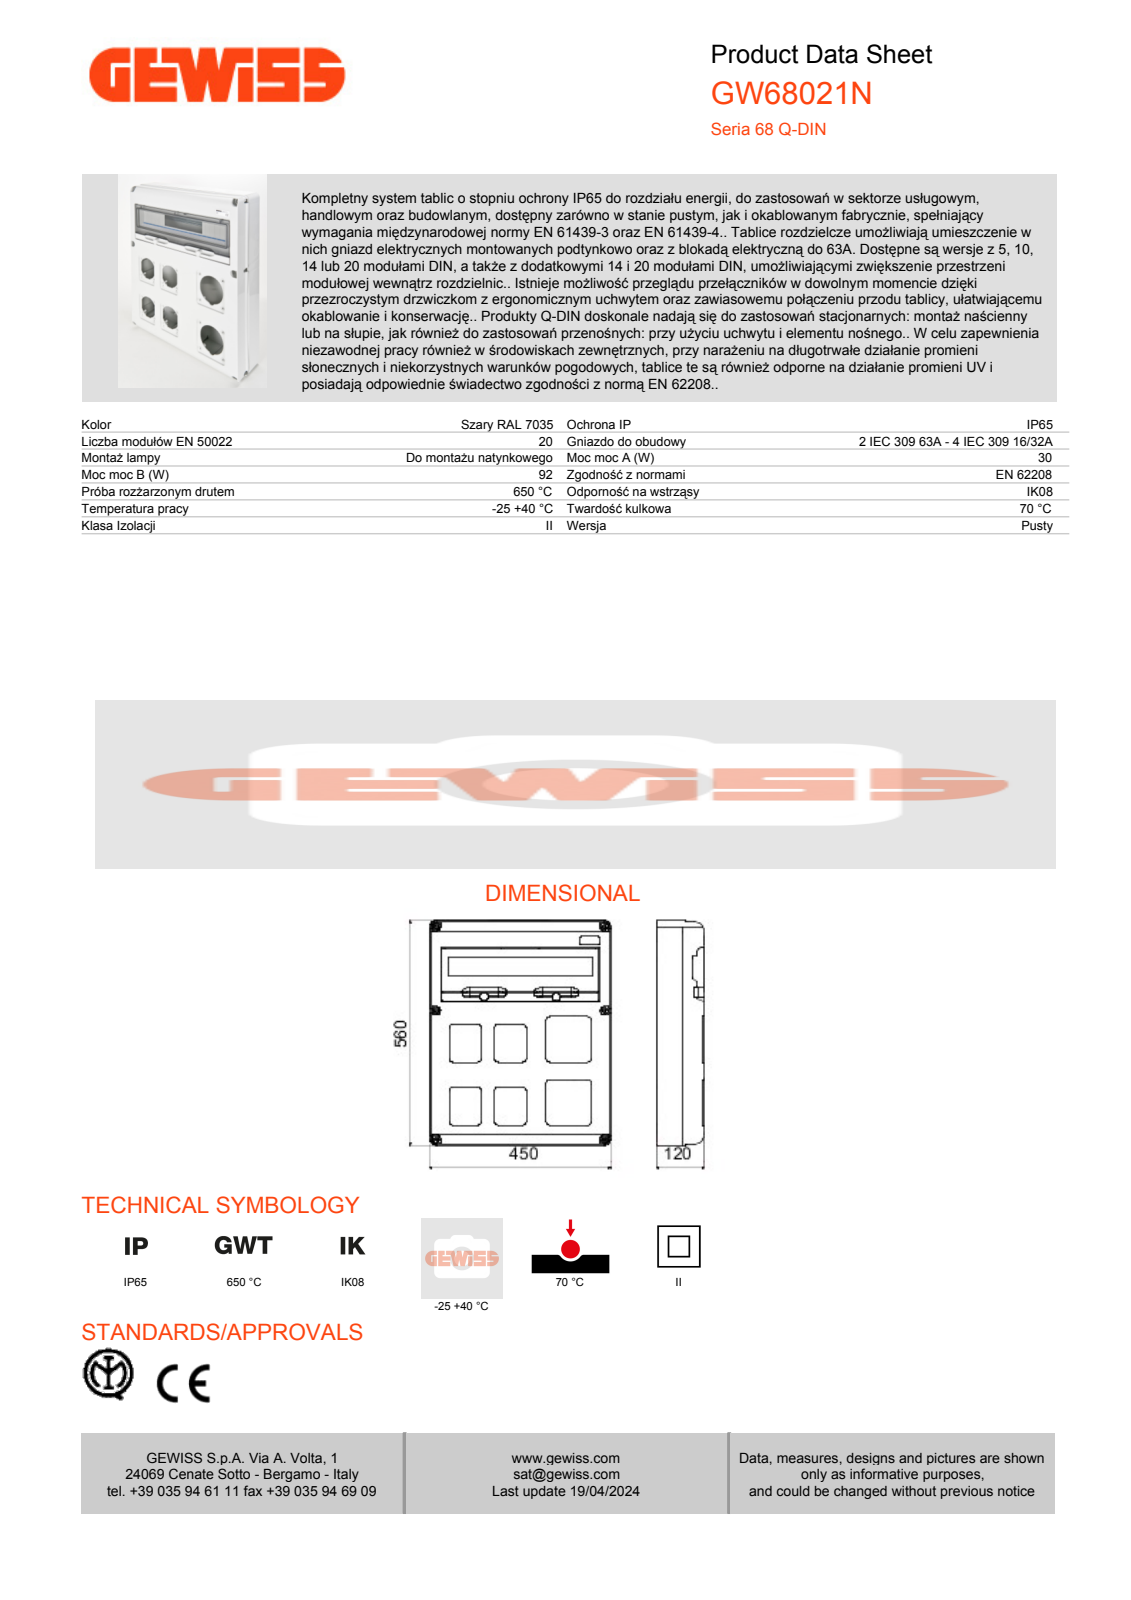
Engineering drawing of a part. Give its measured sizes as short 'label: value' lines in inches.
name: 55523526CXXX___FONDO_QDIN_20M; 5523575H_FR_QDIN_20M_4PR_16-32; GW68021N_ASM
written by: CREO PARAMETRIC BY PTC INC, 2020074 (CONFIG_CONTROL_DESIGN)
unit: in
bodies: 2 solids, 1501 faces (786 planar, 231 cylindrical, 484 other)
size: 22.047 × 17.717 × 4.961
volume: 258.6 in³; area: 2 449 in²
rounds: 48× R0.012, 24× R0.079, 20× R0.071, 12× R0.059, 12× R50.974, 8× R0.091, 8× R0.118, 8× R0.197
face distances: 0.118, 4.539, 4.657, 4.421, 0.121, 17.429, 17.308, 17.717, 0.098, 0.217
